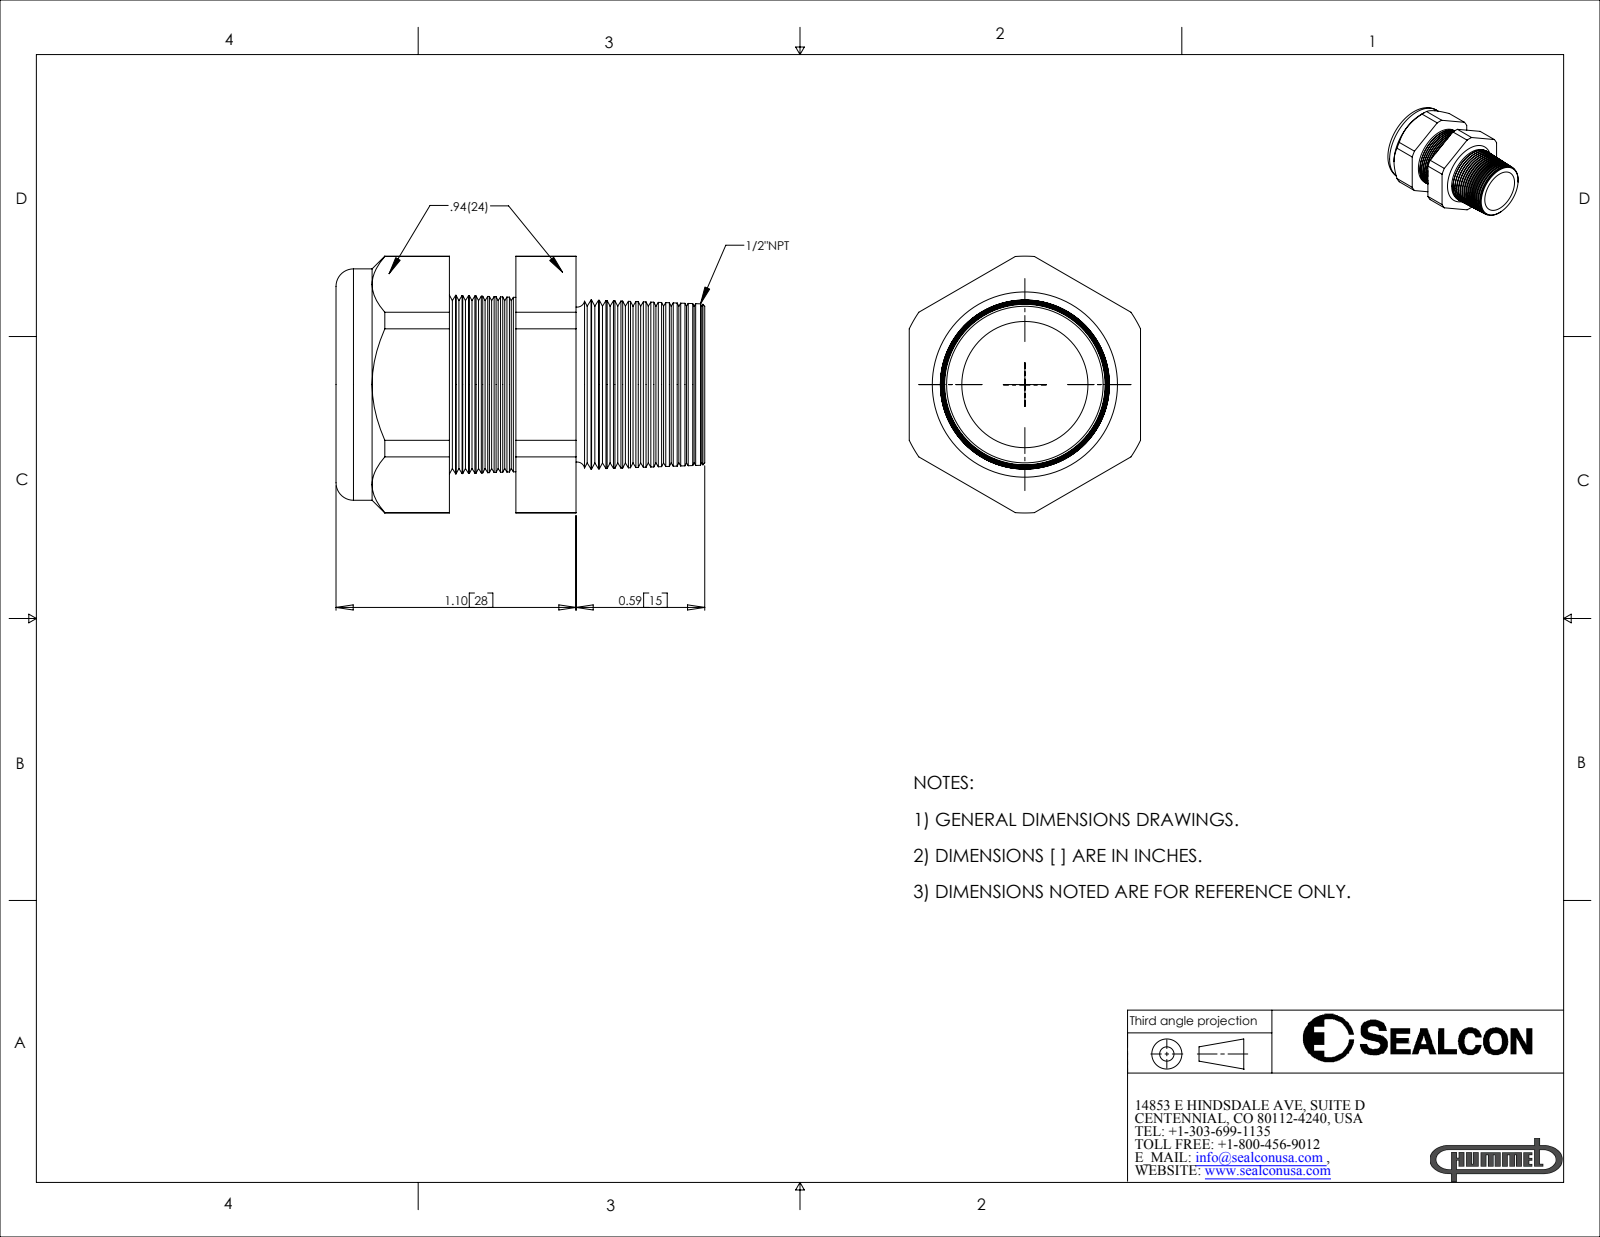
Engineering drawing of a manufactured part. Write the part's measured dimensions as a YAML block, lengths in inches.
part_name: "CD16NP-GY"
step_written_by: "SolidWorks 2007 (CONFIG_CONTROL_DESIGN)"
units: inches
bodies: {solids: 2, faces: 198, planar: 20, cylindrical: 20, other: 158}
overall_size: [1.61, 1.177, 1.06]
volume: 0.763
surface_area: 12.61
round_holes:
  - {diameter: 0.58, count: 1}
  - {diameter: 0.6, count: 1}
round_bosses_or_shafts:
  - {diameter: 1.06, count: 1}
partial_cylinders:
  - {radius: 0.588, count: 1}
face_to_face_distances: [1.06, 0.305, 0.58, 0.276, 0.52, 0.824, 1.1, 0.35, 0.17, 0.474]
